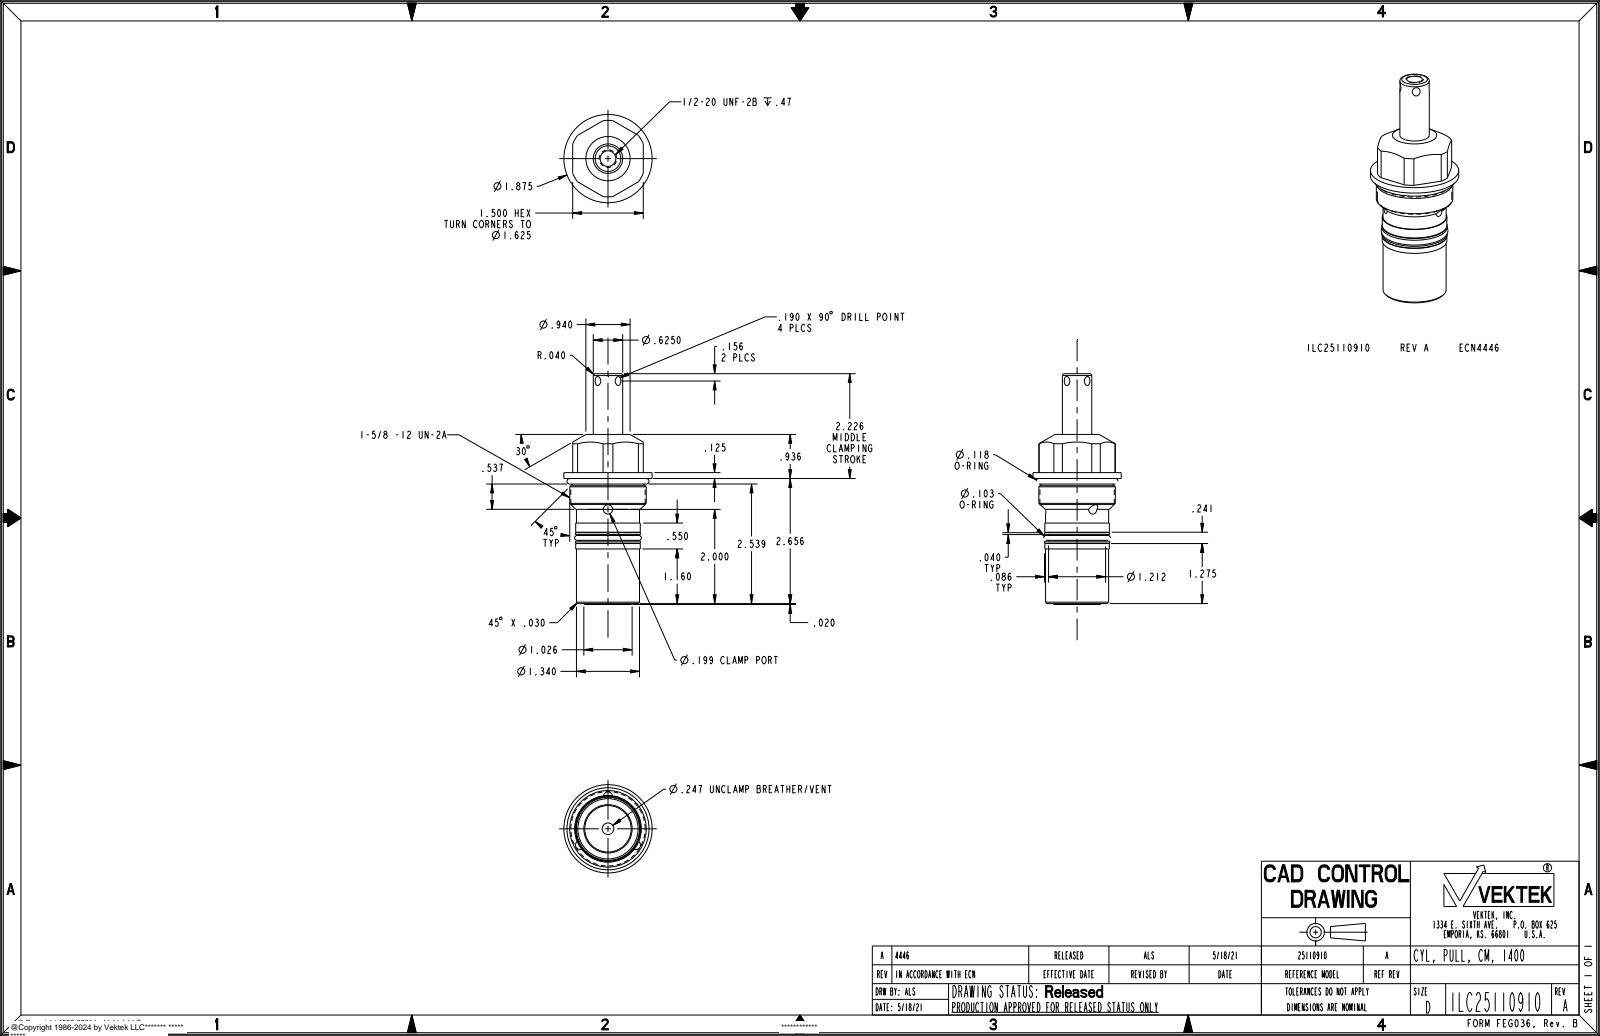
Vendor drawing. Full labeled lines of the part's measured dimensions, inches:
Part name (STEP PRODUCT): ILC25110910
STEP written by: PRO/ENGINEER BY PARAMETRIC TECHNOLOGY CORPORATION, 2013320 (CONFIG_CONTROL_DESIGN)
Units: inches
Bodies: 3 solids, 104 faces (28 planar, 46 cylindrical, 30 other)
Overall size (bounding box): 4.902 × 1.875 × 1.875
Volume: 6.27 in³ · Surface area: 33.13 in²
Round holes (diameter × count): ⌀0.199 ×3, ⌀0.247 ×1, ⌀0.332 ×1
Round bosses / shafts (diameter × count): ⌀1.875 ×1, ⌀1.625 ×1, ⌀1.58 ×1, ⌀1.507 ×1, ⌀1.384 ×1, ⌀1.372 ×1, ⌀1.34 ×1, ⌀1.212 ×1
Main face-to-face distances: 1.5, 0.125, 2.676, 2.801, 0.05, 0.191, 0.02, 2.656, 2.781, 3.612
